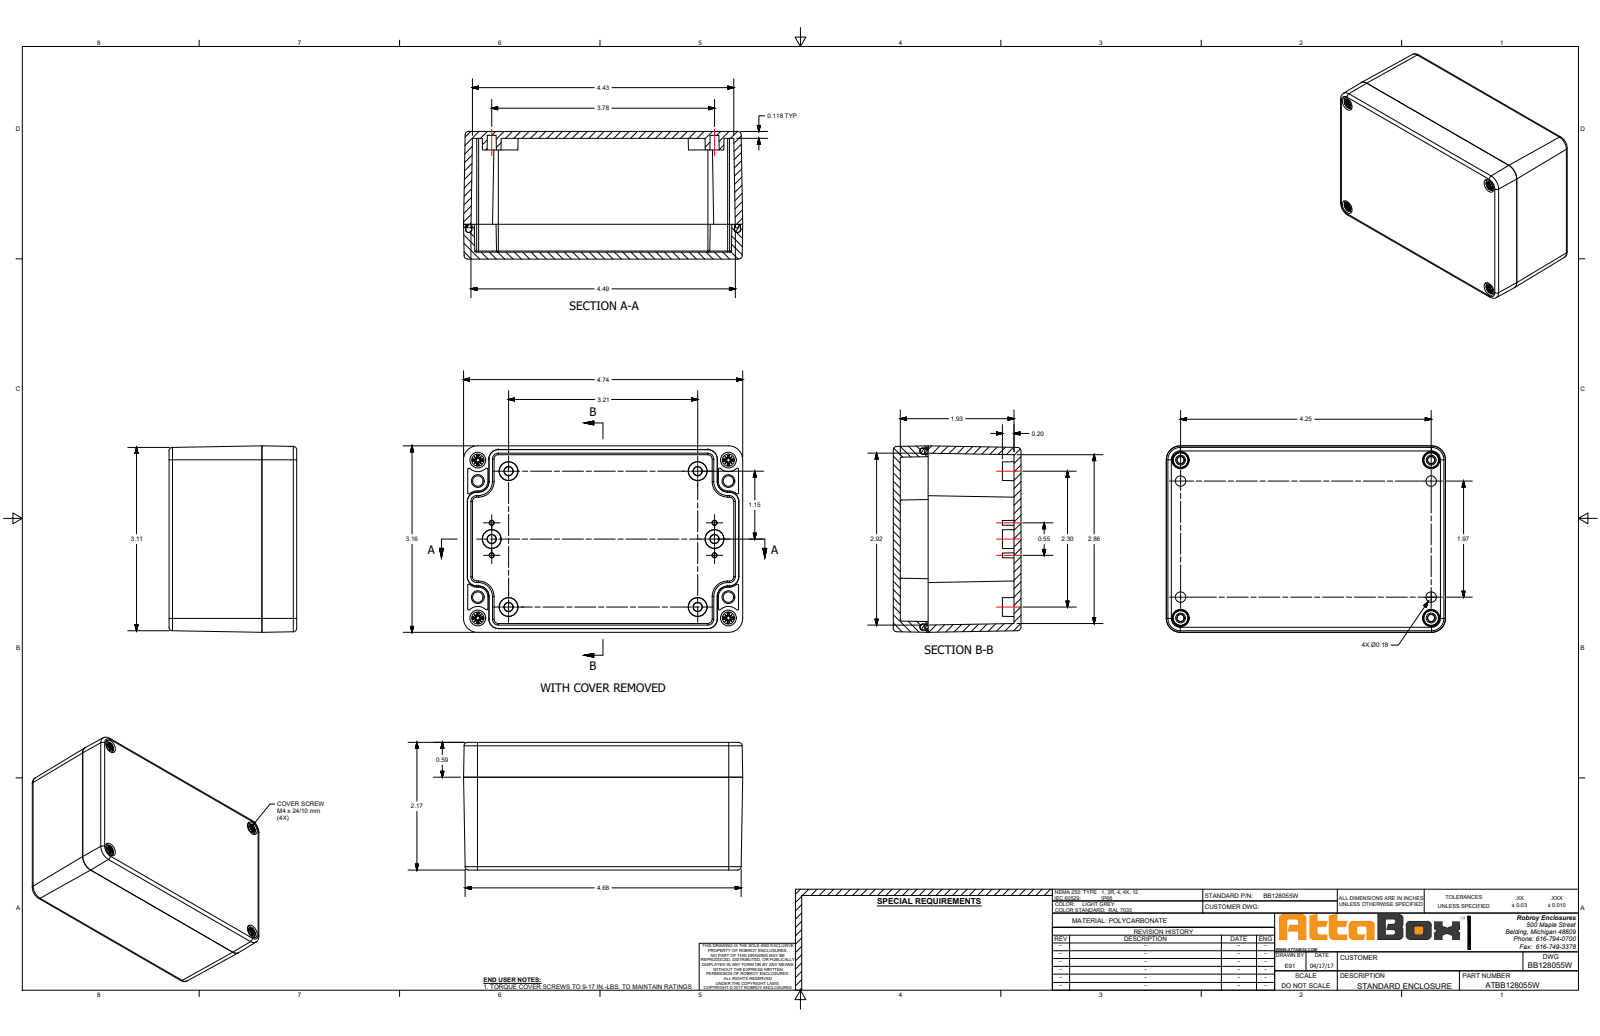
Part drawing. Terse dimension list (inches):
name: BB128055W
written by: SolidWorks 2018 (AUTOMOTIVE_DESIGN)
unit: in
bodies: 11 solids, 1632 faces (611 planar, 431 cylindrical, 590 other)
size: 4.736 × 3.161 × 2.167
volume: 8.31 in³; area: 153 in²
holes: 8× ⌀0.177, 4× ⌀0.128, 4× ⌀0.189, 4× ⌀0.201, 4× ⌀0.276, 4× ⌀0.291, 4× ⌀0.295
bosses: 4× ⌀0.268, 4× ⌀0.173, 4× ⌀0.157, 4× ⌀0.13
rounds: 35× R0.02, 32× R0.043, 16× R0.039, 8× R0.059, 8× R0.083, 8× R0.185, 4× R0.102, 4× R0.11
face distances: 0.118, 2.047, 2.165, 1.929, 0.124, 3.161, 3.037, 0.183, 0.126, 0.472
hole spacings: 0.354, 2.323, 4.252, 4.267, 4.845, 1.969, 2.677, 4.685
